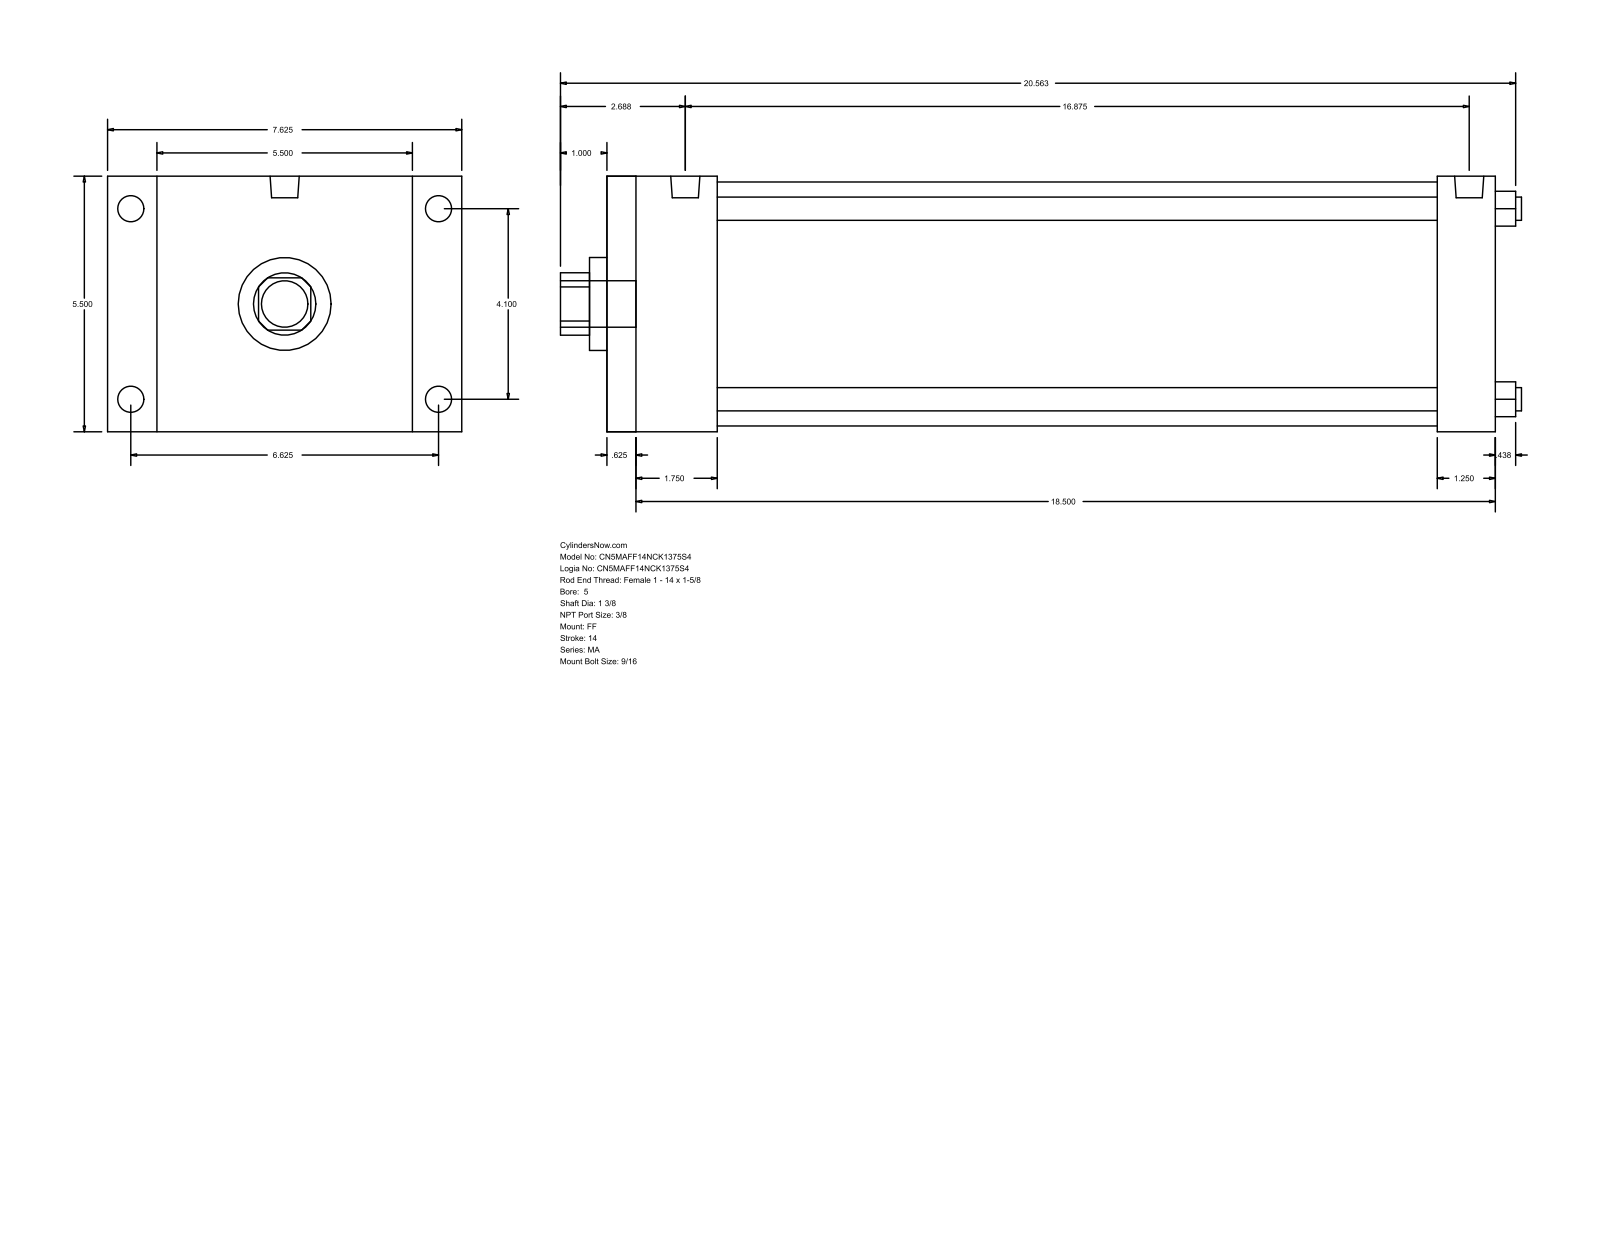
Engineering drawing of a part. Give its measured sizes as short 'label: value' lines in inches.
name: MA_FF__0500_1.375
written by: GSSL Pune (CONFIG_CONTROL_DESIGN)
unit: in
bodies: 0 solids, 92 faces (64 planar, 28 cylindrical, 0 other)
size: 20.687 × 7.625 × 5.5
holes: 4× ⌀0.5, 1× ⌀1.375, 1× ⌀2, 1× ⌀5.25
bosses: 4× ⌀0.563, 4× ⌀0.437, 2× ⌀0.627, 1× ⌀1
rounds: 1× R0.672
face distances: 5.5, 19.125, 0.625, 18.5, 17.875, 17.25, 1.25, 2.375, 1.75, 15.5
hole spacings: 2.899, 4.1, 5.798
